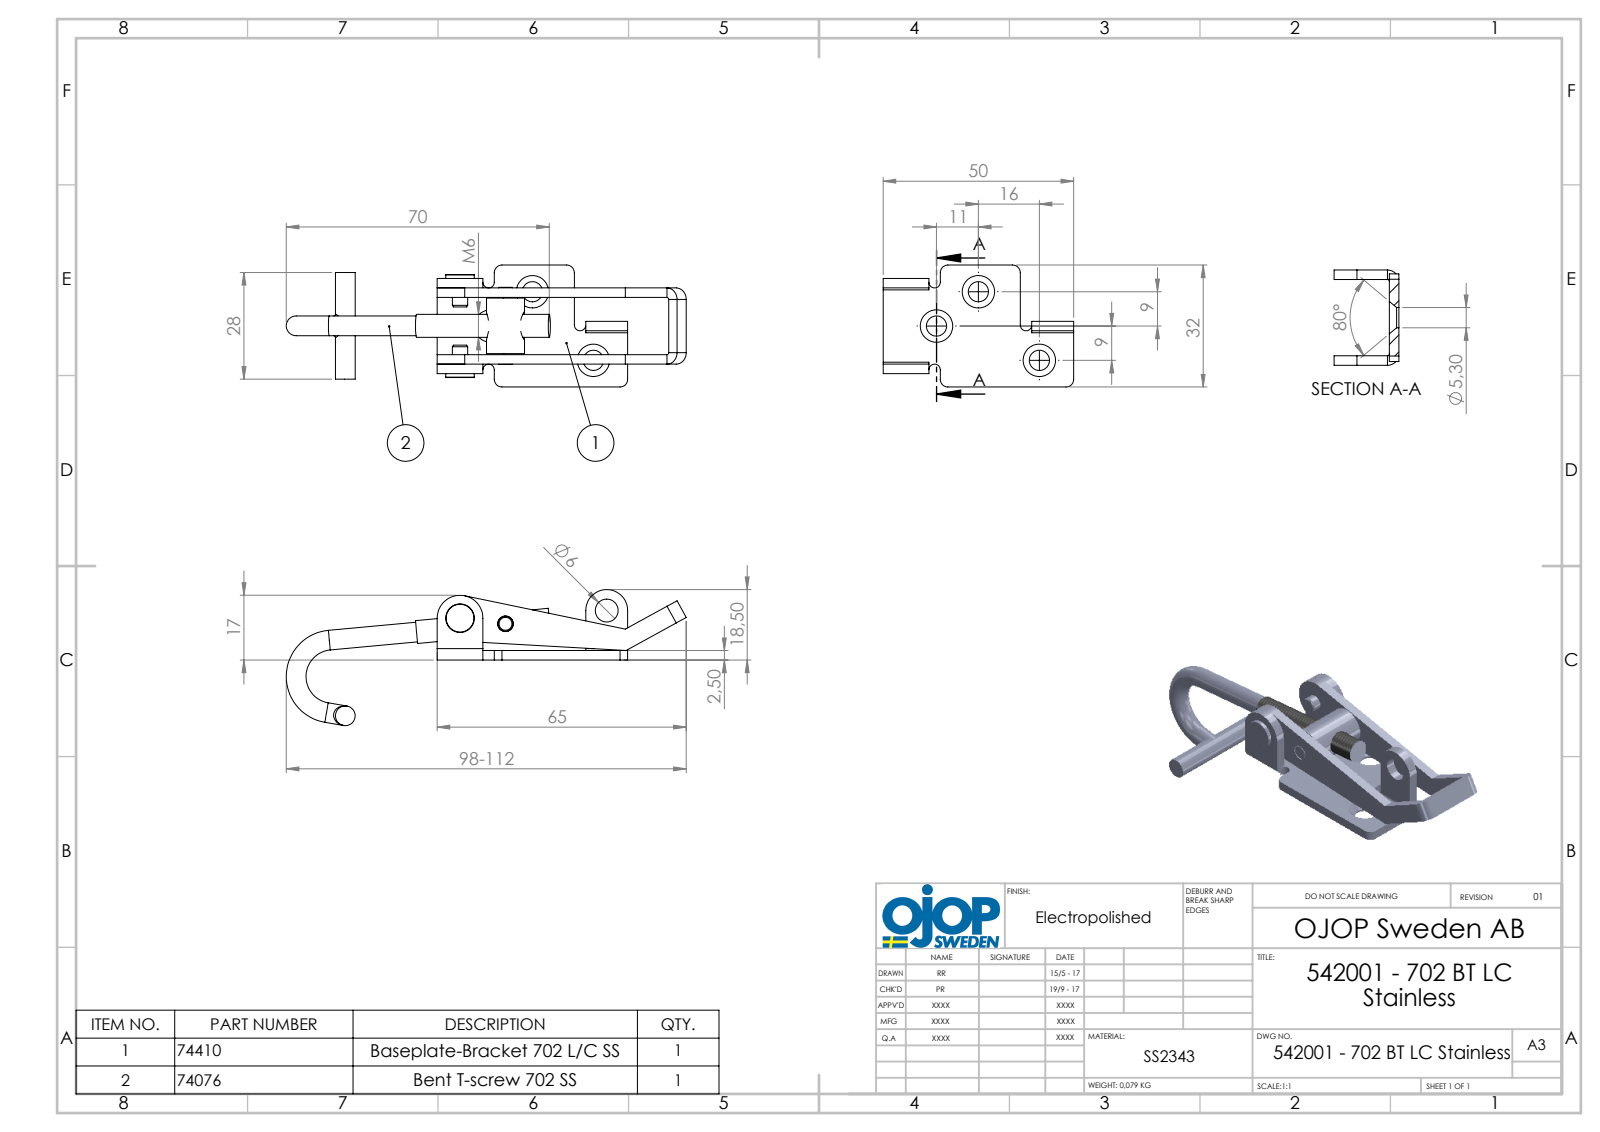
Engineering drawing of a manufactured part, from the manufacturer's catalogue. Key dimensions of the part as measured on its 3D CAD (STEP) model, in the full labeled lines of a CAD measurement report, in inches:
Part name (STEP PRODUCT): 702 - Ansatsnit; 702 - Böjd T-skruv M6; 542001 - 702 BT LC Stainless; 702 - Rulle (+2 more)
STEP written by: SolidWorks 2015 (AUTOMOTIVE_DESIGN)
Units: inches
Bodies: 6 solids, 164 faces (66 planar, 72 cylindrical, 26 other)
Overall size (bounding box): 4.228 × 1.26 × 1.079
Volume: 0.645 in³ · Surface area: 15.93 in²
Round holes (diameter × count): ⌀0.209 ×3, ⌀0.161 ×2, ⌀0.236 ×2, ⌀0.197 ×1
Round bosses / shafts (diameter × count): ⌀0.204 ×3, ⌀0.157 ×2, ⌀0.394 ×1, ⌀0.295 ×1, ⌀0.236 ×1
Partial cylindrical surfaces — rounded edges, fillets, slot ends (radius × count): R0.02 ×5, R0.118 ×5, R0.079 ×4, R0.059 ×2, R0.059 ×1, R0.217 ×1, R0.236 ×1
Main face-to-face distances: 0.098, 0.689, 0.787, 0.344, 0.443, 0.591, 0.197, 0.246, 0.886, 0.236
Hole centre spacings: 0.473, 0.559, 0.948, 1.055, 1.12, 1.518
